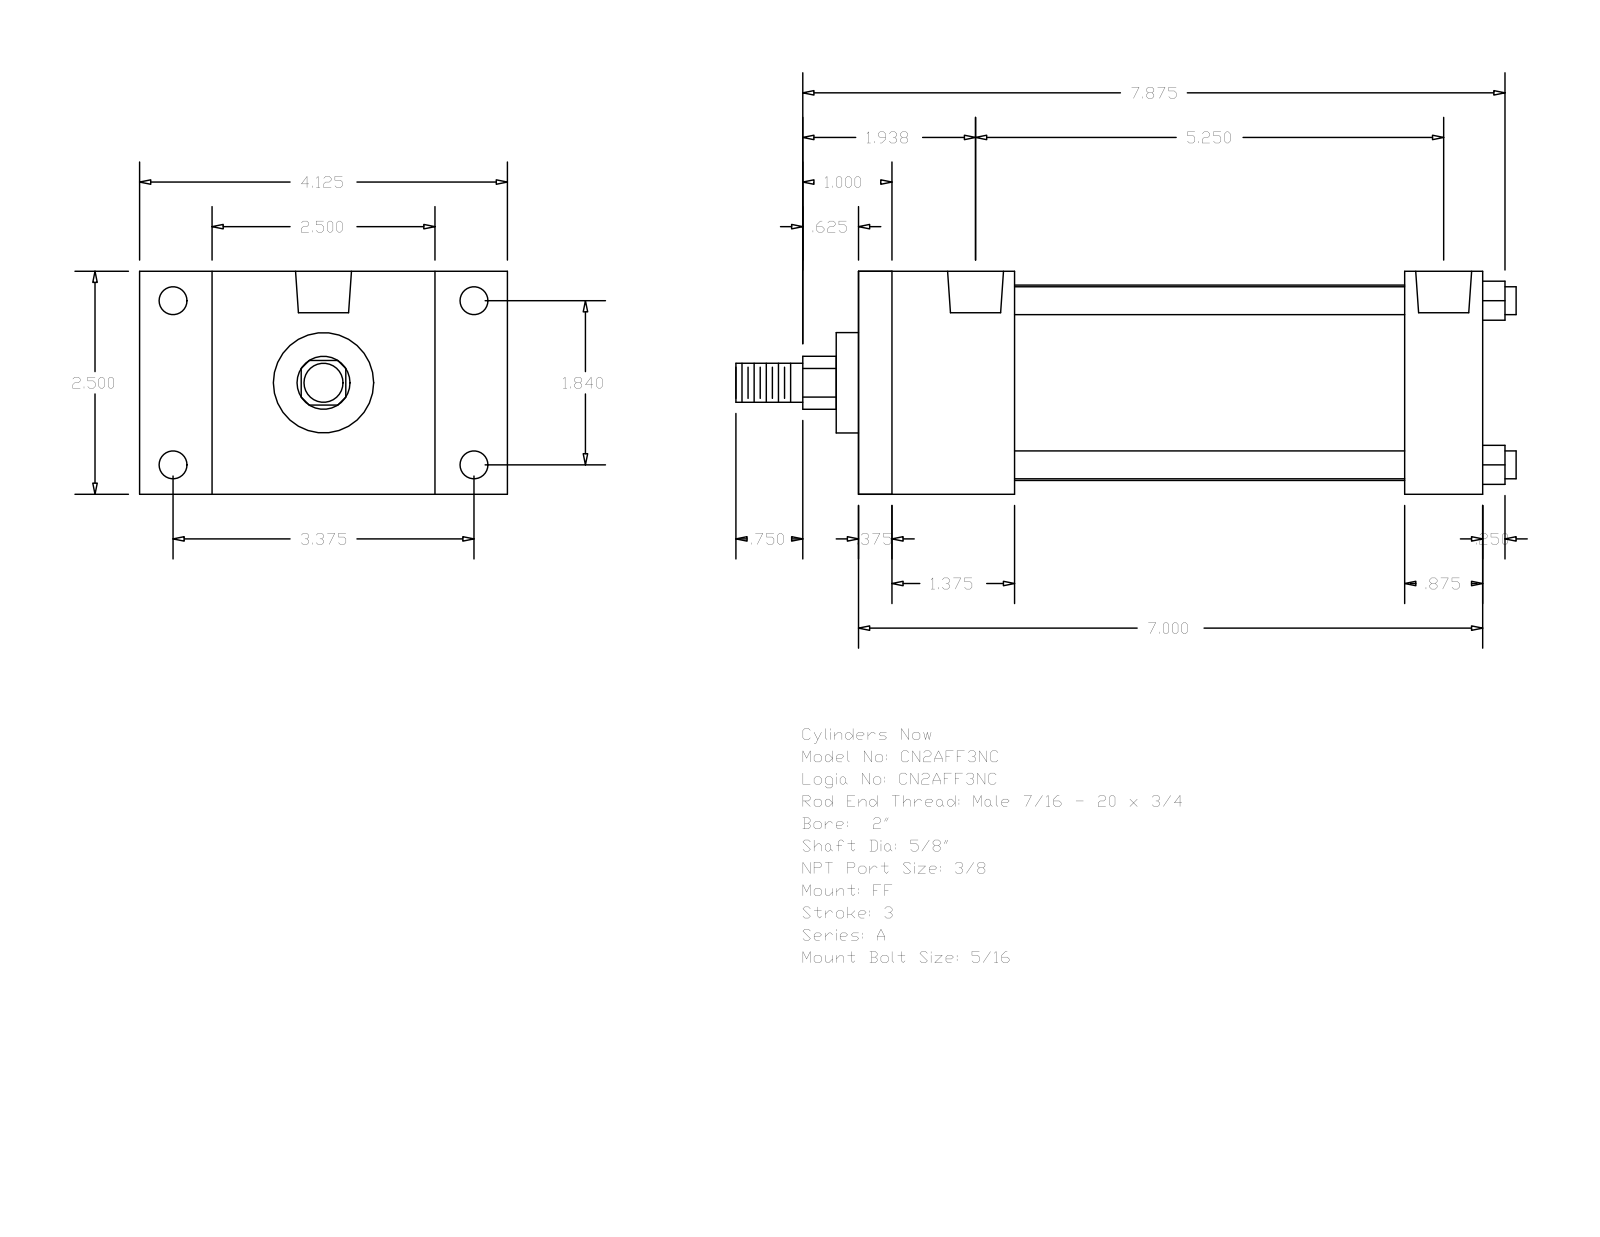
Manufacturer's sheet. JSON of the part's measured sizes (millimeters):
{"part_name": "A_FF__0200_0.625", "step_written_by": "GSSL Pune (CONFIG_CONTROL_DESIGN)", "units": "millimeters", "bodies": {"solids": 0, "faces": 92, "planar": 64, "cylindrical": 28, "other": 0}, "overall_size": [222.25, 104.78, 63.5], "round_holes": [[5.56, 4], [7.94, 4], [15.93, 2]], "round_bosses_or_shafts": [[7.94, 4], [55.63, 1], [28.57, 1], [15.88, 1], [11.11, 1]], "partial_cylinders_radius": [[7.54, 1]], "face_to_face_distances": [63.5, 177.8, 9.52, 168.28, 34.93, 44.45, 155.57, 146.05, 111.12, 133.35], "hole_center_spacings": [46.74, 85.72, 97.63, 125.4, 3.97, 3.98, 129.37, 129.38]}
